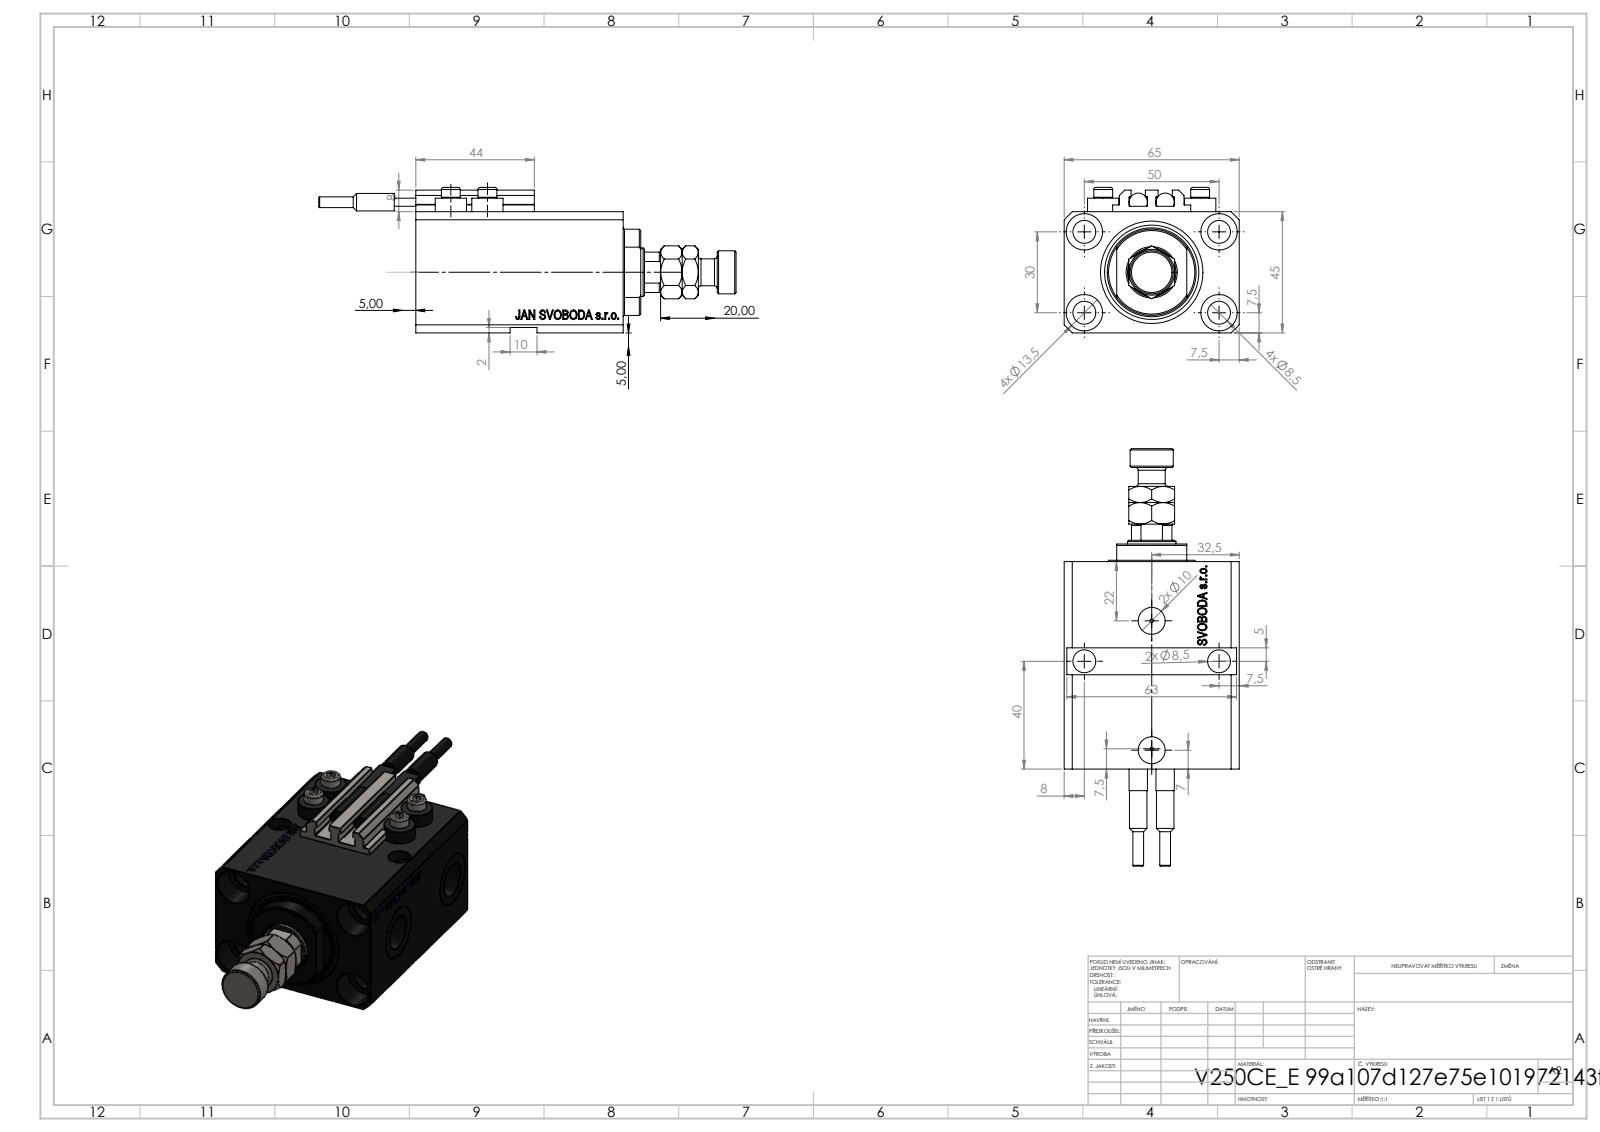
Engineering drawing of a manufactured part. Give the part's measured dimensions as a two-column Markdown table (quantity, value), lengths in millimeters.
| quantity | value |
| --- | --- |
| part name | SWITCH_V250CE; V250CE_VC_E; V250CE_E_Body; MFA (+2 more) |
| STEP written by | SolidWorks 2019 (CONFIG_CONTROL_DESIGN) |
| units | millimeters |
| bodies | 11 solids, 1171 faces (559 planar, 142 cylindrical, 470 other) |
| overall size | 155 × 65 × 54 |
| volume | 208 774 mm³ |
| surface area | 64 000 mm² |
| round holes (diameter × count) | 8.5 × 7, 1.25 × 4, 4 × 4, 13.5 × 4, 10 × 2, 13.16 × 2, 20 × 2, 18 × 1, 25 × 1, 38 × 1 |
| round bosses / shafts (diameter × count) | 11.6 × 4, 7 × 4, 6.8 × 2, 6.5 × 2, 4 × 2, 16 × 1, 10 × 1 |
| partial cylindrical surfaces (radius × count) | 0.2 × 10, 8.5 × 1, 16 × 1 |
| main face-to-face distances | 45, 65, 14, 63, 2, 77, 3, 6.9, 47, 5 |
| hole center spacings | 29.15, 50, 13.6, 15.12, 18.81, 18.97, 26.22, 26.61 |
